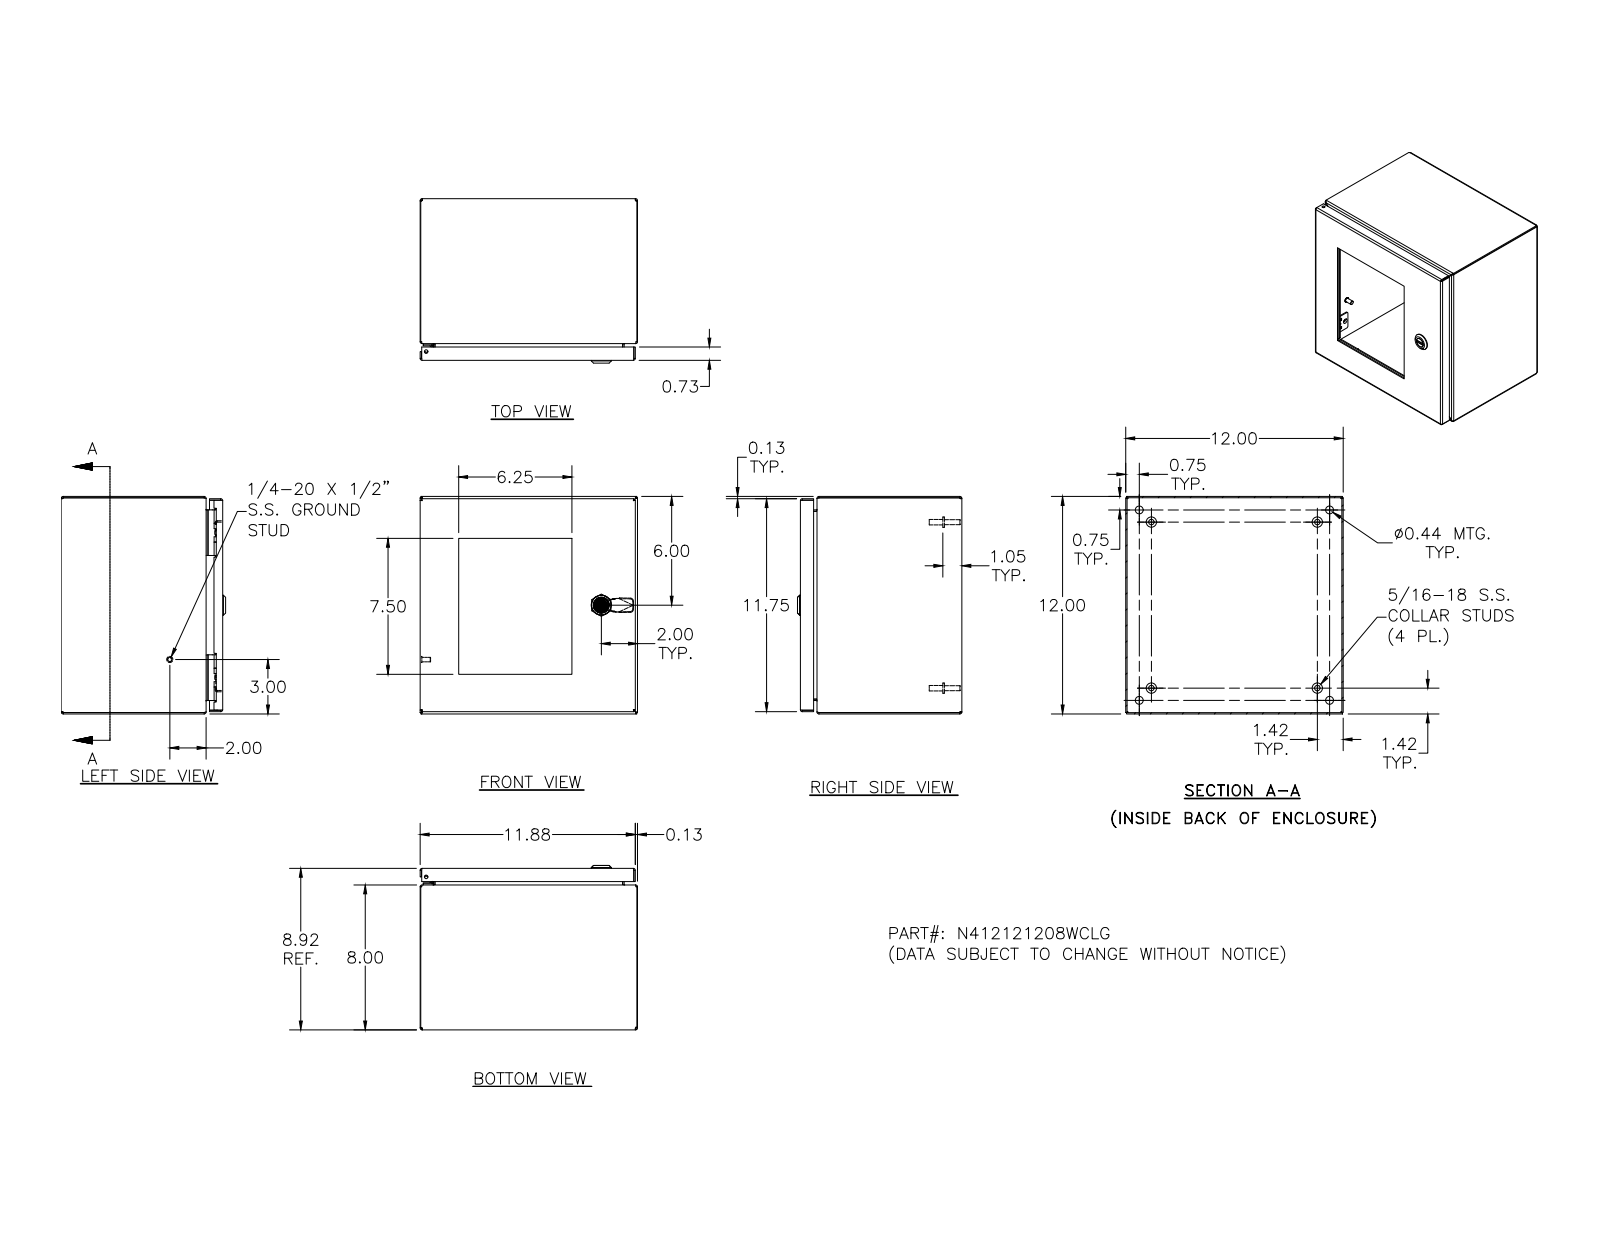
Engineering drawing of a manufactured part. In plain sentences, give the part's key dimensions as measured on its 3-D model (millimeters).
The part is named "N412121208WCLG". Its 3-D file was written by "SolidWorks 2018 (AUTOMOTIVE_DESIGN)". It is 53 solids with 1763 faces: 665 planar, 585 cylindrical and 513 other. Overall it measures 304.8 by 304.8 by 230.5 millimeters. Its volume is 1 183 000 cubic millimeters and its surface area 1 090 000 square millimeters. Round holes: 10 of diameter 4, 8 of diameter 7.1, 5 of diameter 4.8, 4 of diameter 2.4, 4 of diameter 3.9, 4 of diameter 4.2, 4 of diameter 4.4, 4 of diameter 11.1, 1 of diameter 4.7, 1 of diameter 5, 1 of diameter 8, 1 of diameter 10. Round bosses or shafts: 10 of diameter 6.4, 8 of diameter 8.6, 8 of diameter 4.8, 4 of diameter 14.3, 4 of diameter 9.1, 4 of diameter 8.1, 4 of diameter 7.6, 4 of diameter 7. Partial cylindrical surfaces (rounded edges, fillets, slot ends): 34 of radius 0.8, 30 of radius 0.3, 26 of radius 1.3, 24 of radius 2.7, 18 of radius 0.4, 16 of radius 3.2, 13 of radius 0.5, 8 of radius 0.8. The main face-to-face distances are 1.9, 302.9, 224.6, 304.8, 301, 222.7, 226.5, 6.4, 218.3, 216.4. The hole center spacings are 203.2, 101.6, 158, 218.1, 266.7, 226.7, 12.7, 16.7.
